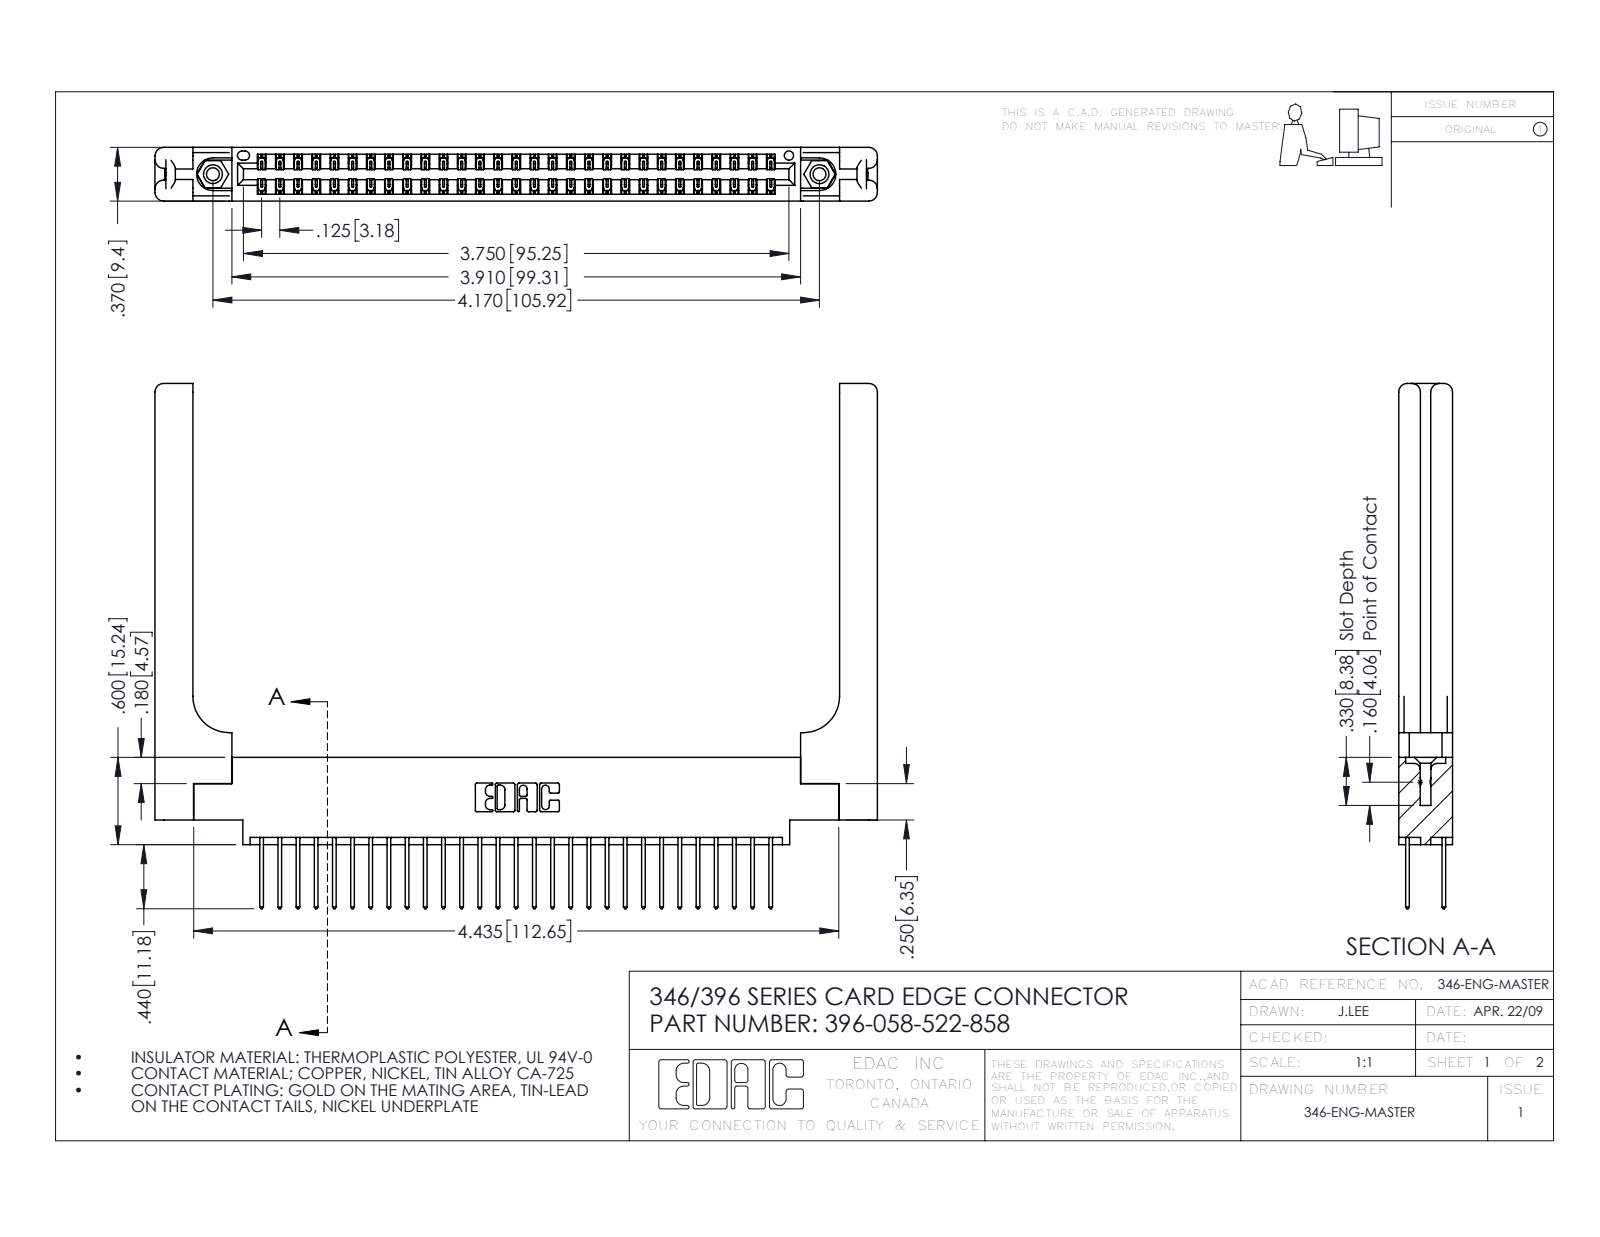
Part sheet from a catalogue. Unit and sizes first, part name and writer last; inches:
Units: inches
Overall size (bounding box): 4.966 × 3.61 × 0.37
Round holes (diameter × count): ⌀0.089 ×2, ⌀0.125 ×2, ⌀0.156 ×2, ⌀0.064 ×1
Round bosses / shafts (diameter × count): ⌀0.155 ×2
Partial cylindrical surfaces — rounded edges, fillets, slot ends (radius × count): R0.006 ×87, R0.01 ×58, R0.01 ×22, R0.06 ×16, R0.007 ×6, R0.031 ×6, R0.026 ×3, R0.014 ×2
Main face-to-face distances: 0.37, 0.048, 0.322, 0.072, 0.25, 0.15, 0.148, 0.025, 0.298, 0.275
Hole centre spacings: 0.246, 3.962, 4.17
Volume: 1.201 in³ · Surface area: 34.72 in²
Bodies: 63 solids, 3398 faces (2258 planar, 1080 cylindrical, 60 other)
Part name (STEP PRODUCT): 346-220-058_345-220-058; 345-292-001_345-293-122; 396-058-522-858; 346 Part_0.170 Offset - 0.156 Dia-TH (+1 more)
STEP written by: SolidWorks 2016 (CONFIG_CONTROL_DESIGN)
